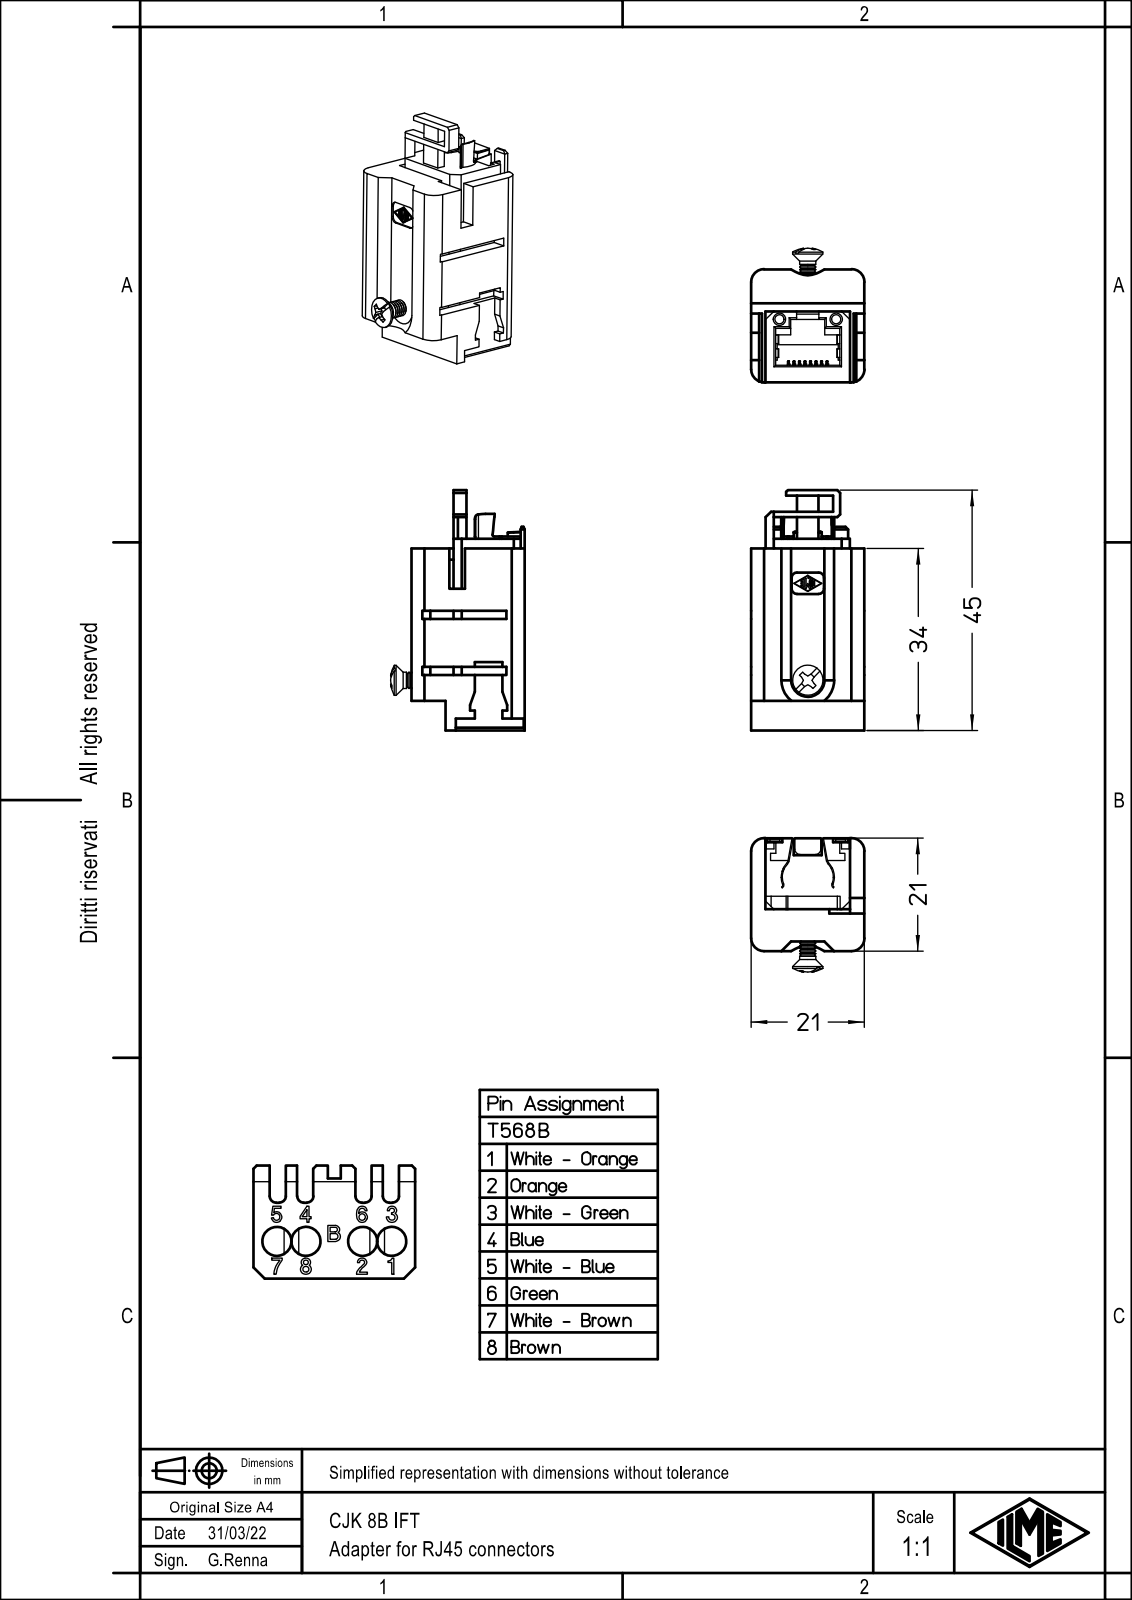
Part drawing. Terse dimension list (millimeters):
name: CJK_8B_IFT
written by: Creo Elements/Direct Modeling 20.1B 02-Apr-2019 (C) Parametric Technology GmbH (AUTOMOTIVE_DESIGN)
unit: mm
bodies: 1 solid, 360 faces (267 planar, 51 cylindrical, 42 other)
size: 44.6 × 24.89 × 21
volume: 10 593 mm³; area: 8 127 mm²
holes: 2× ⌀1.7
bosses: 1× ⌀5.6, 1× ⌀3
rounds: 15× R0.1, 8× R1, 4× R2.4, 3× R3.5, 2× R0.4, 2× R0.6, 2× R0.8, 2× R3.7
face distances: 2.7, 15.65, 18.3, 2.65, 18.35, 1.5, 15.7, 15.6, 21, 13.19
hole spacings: 10.5
